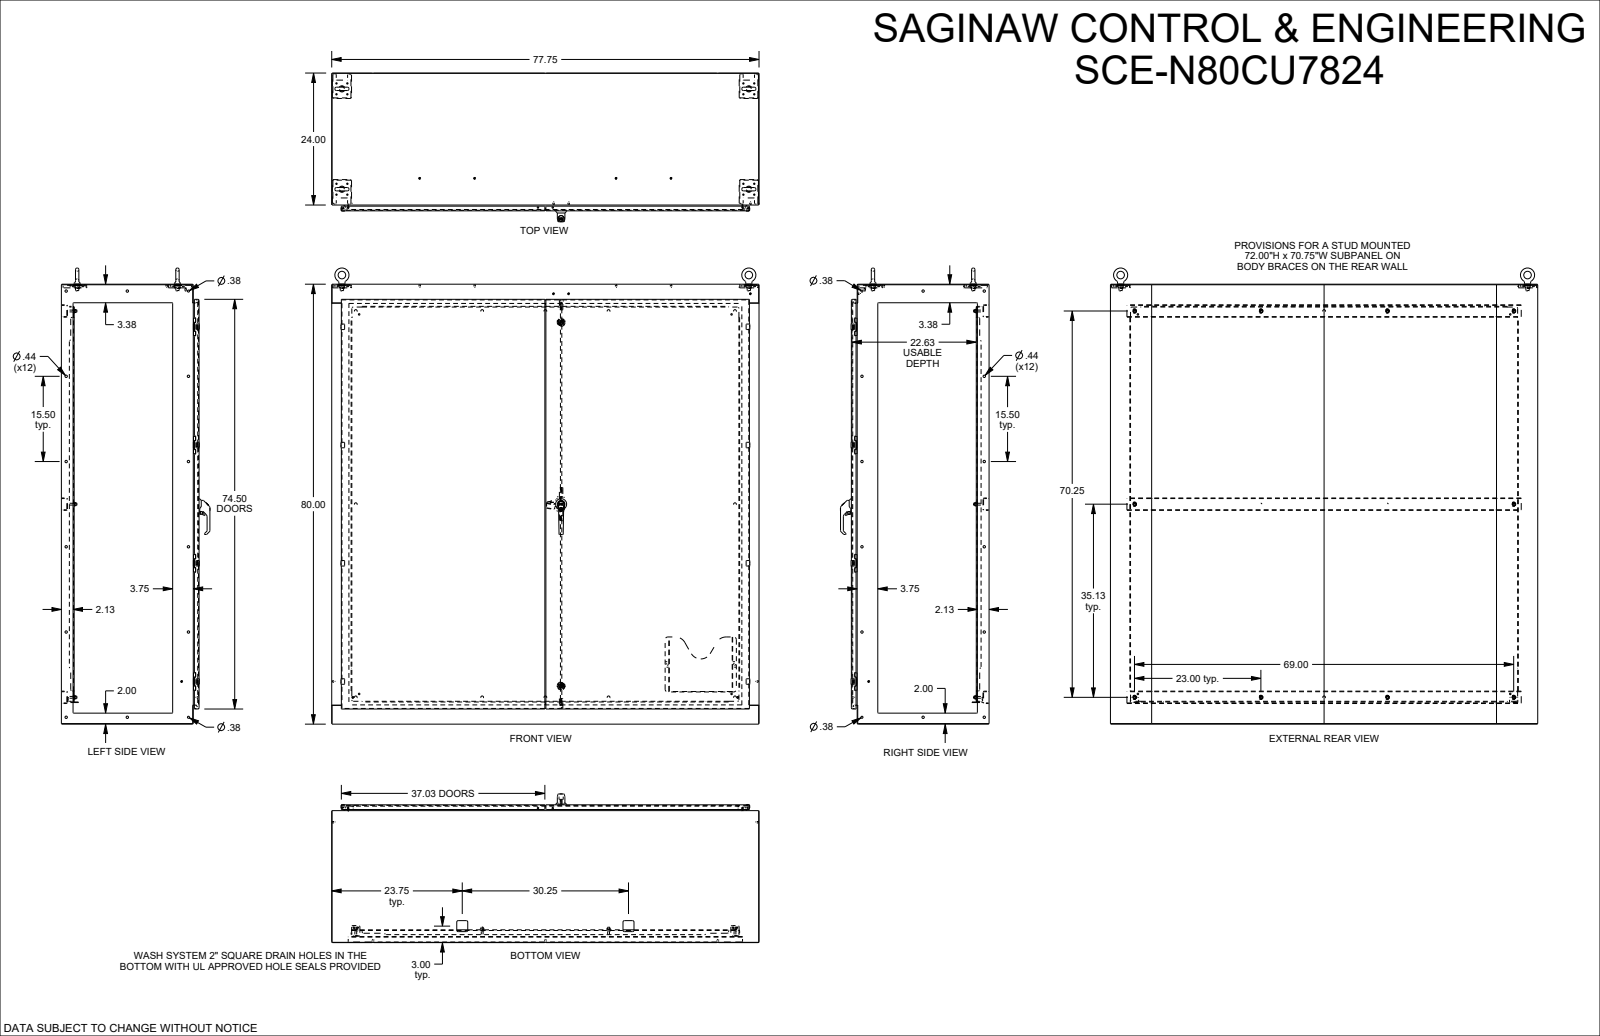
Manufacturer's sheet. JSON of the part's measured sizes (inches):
{"part_name": "SCE-N80CU7824", "step_written_by": "SolidWorks 2023 (AUTOMOTIVE_DESIGN)", "units": "inches", "bodies": {"solids": 49, "faces": 8424, "planar": 3374, "cylindrical": 2741, "other": 2309}, "overall_size": [82.945, 77.75, 27.046], "volume_in3": 2123, "surface_area_in2": 40344, "round_holes": [[0.25, 20], [0.375, 18], [0.205, 16], [0.244, 16], [0.437, 12], [0.04, 8], [0.17, 8], [0.218, 8], [0.256, 4], [0.343, 4], [0.344, 4], [0.36, 4]], "round_bosses_or_shafts": [[0.17, 24], [0.25, 20], [0.24, 16], [0.196, 10], [1.4, 4], [1.173, 4], [0.6, 4], [0.341, 4]], "partial_cylinders_radius": [[0.015, 292], [0.03, 200], [0.125, 100], [0.02, 74], [0.02, 48], [0.25, 48], [0.039, 42], [0.04, 40]], "face_to_face_distances": [0.104, 24.954, 25.058, 24.85, 79.896, 23.896, 1.058, 80, 79.792, 23.792], "hole_center_spacings": [1.979, 15.5, 27.117, 43, 1.4, 21.5, 31, 38.159]}
